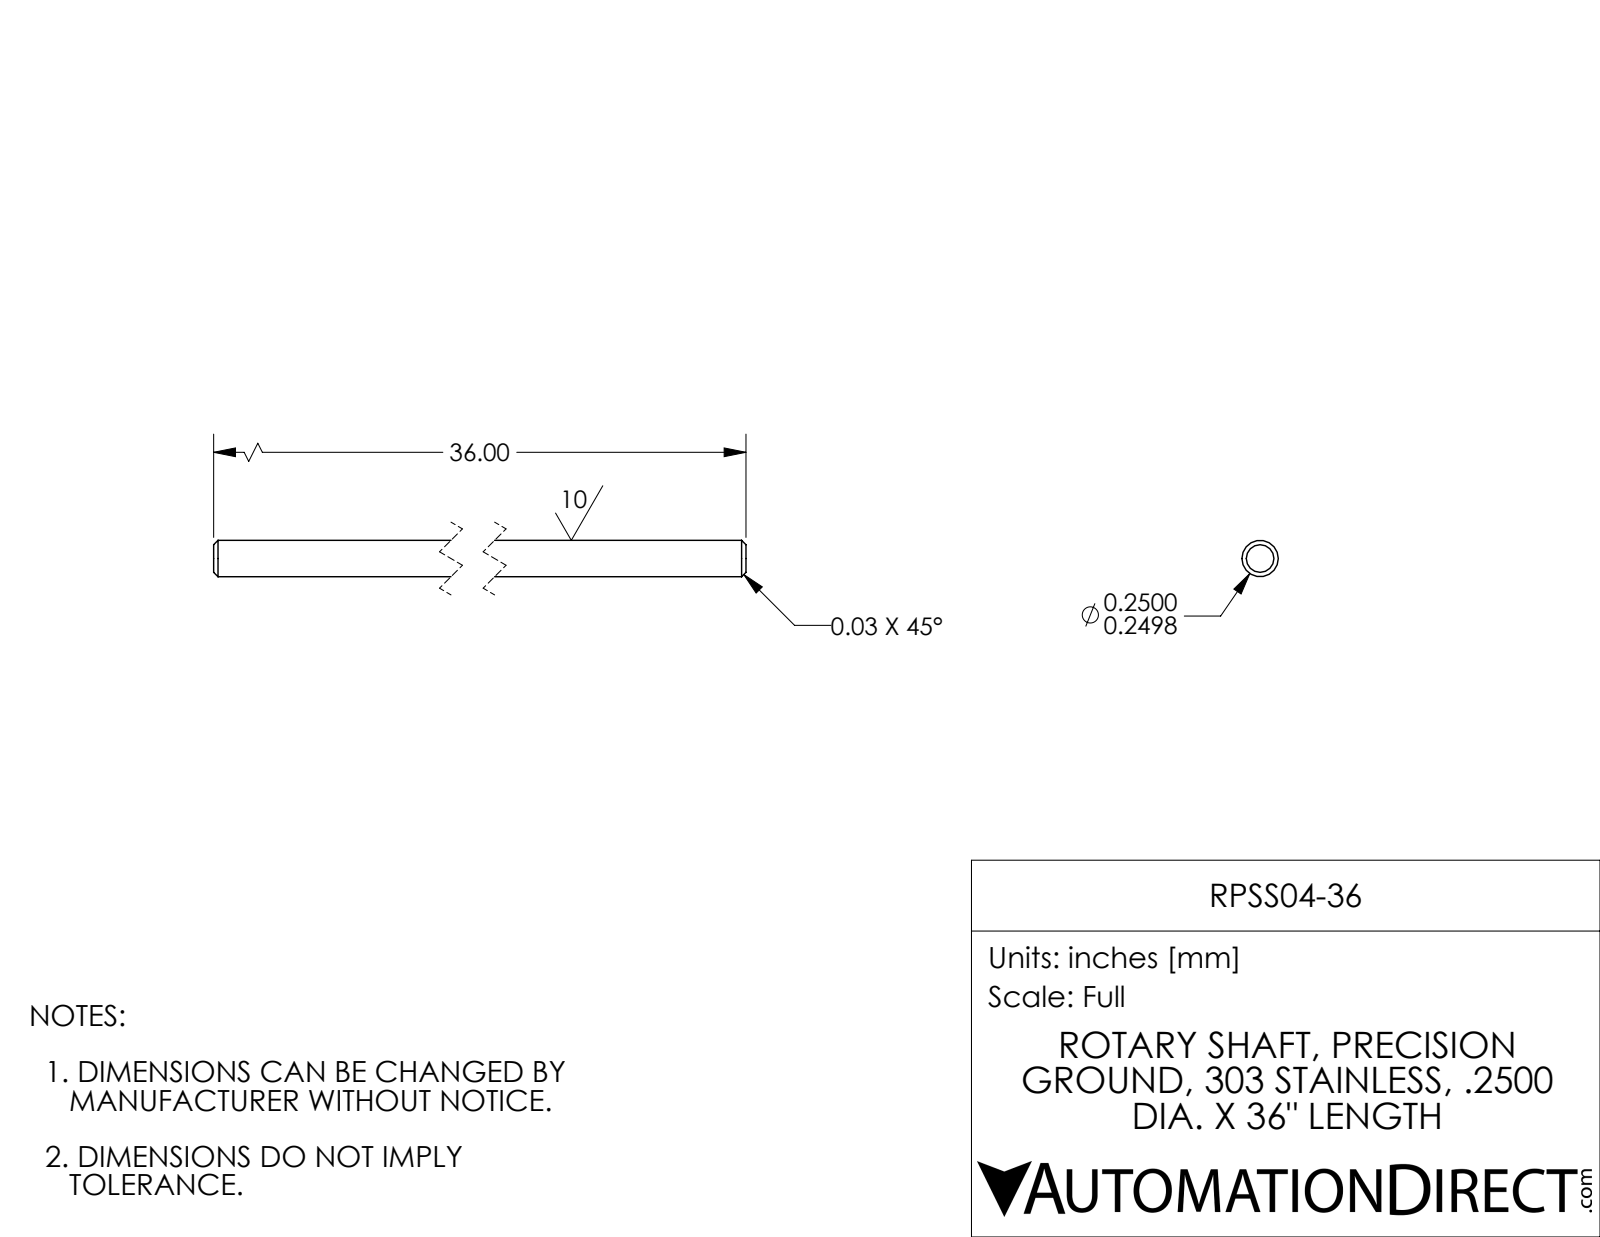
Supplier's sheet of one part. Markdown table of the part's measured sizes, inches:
| quantity | value |
| --- | --- |
| part name | RPSS04-36 |
| STEP written by | SolidWorks 2017 (AUTOMOTIVE_DESIGN) |
| units | inches |
| bodies | 1 solid, 8 faces (2 planar, 2 cylindrical, 4 other) |
| overall size | 36 × 0.25 × 0.25 |
| volume | 1.766 in³ |
| surface area | 28.34 in² |
| round bosses / shafts (diameter × count) | 0.25 × 1 |
| main face-to-face distances | 36 |
